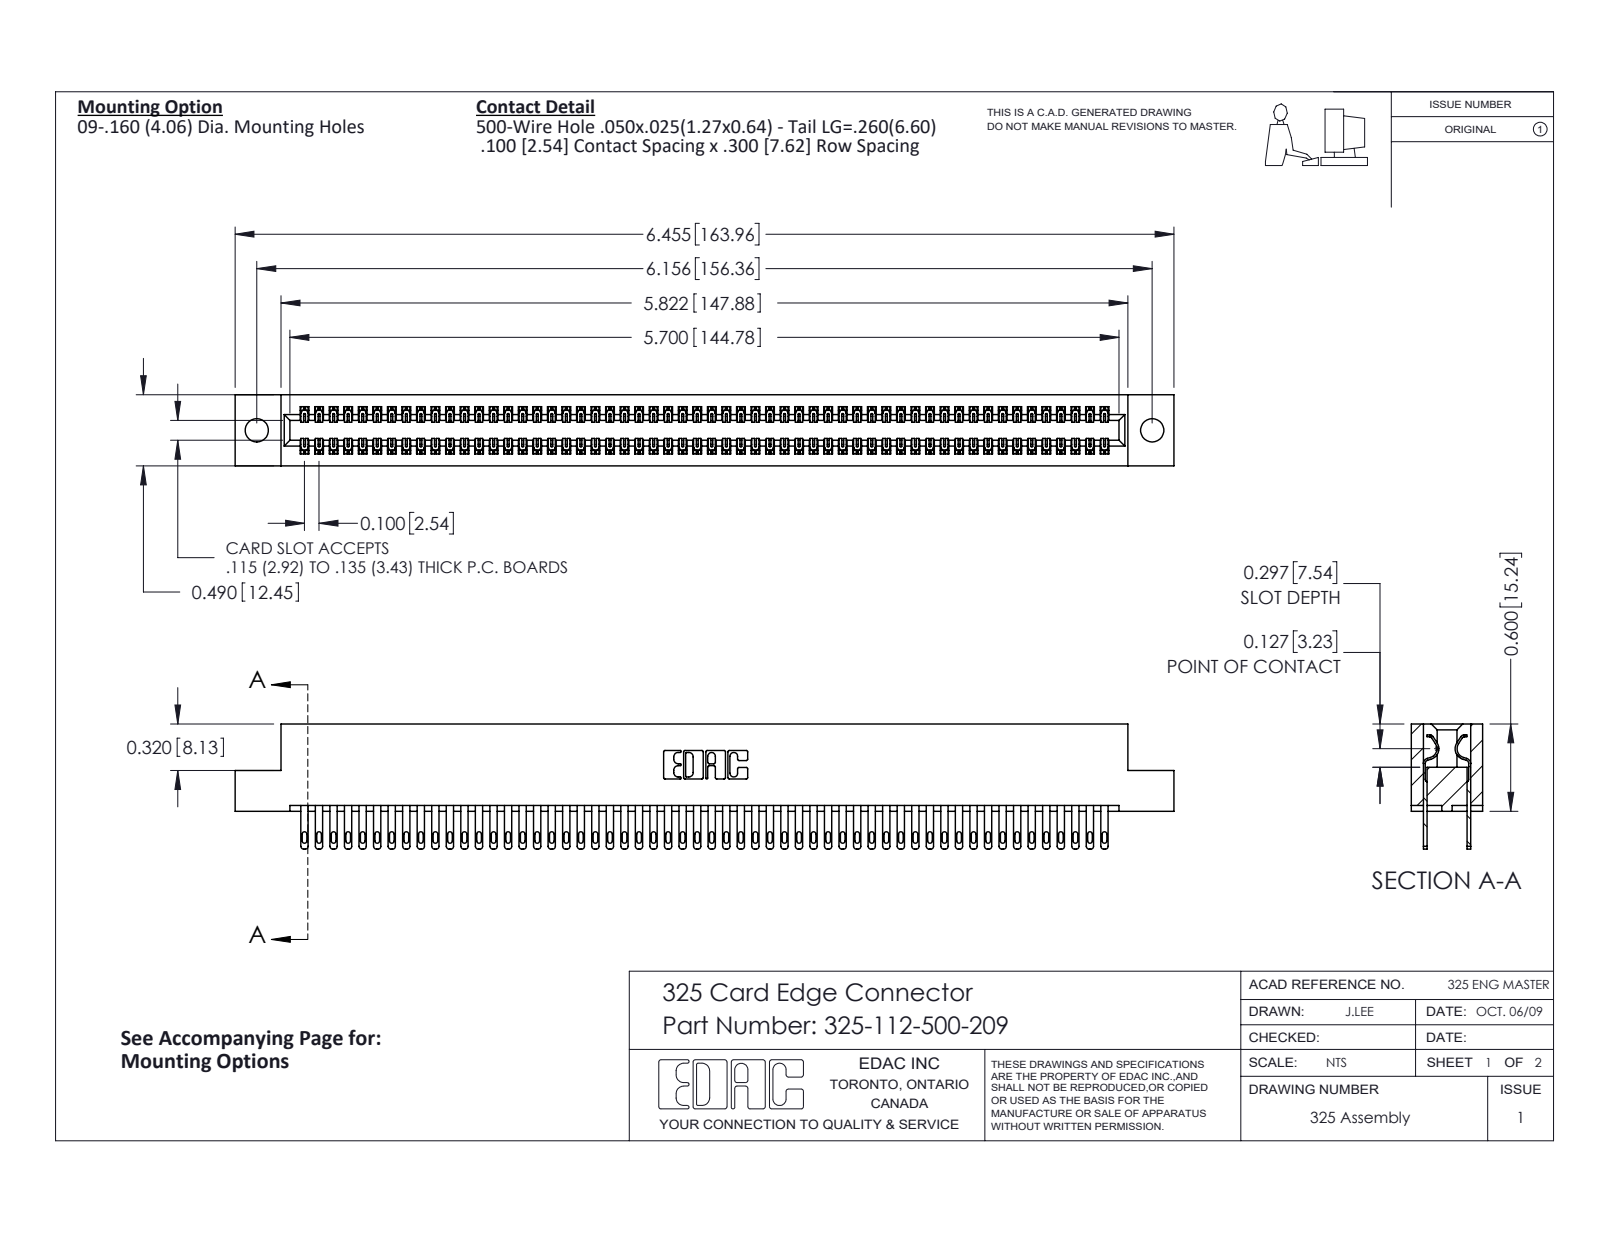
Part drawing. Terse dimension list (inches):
name: 325 Part_.160 TH; 325-112-500-209; 325-292-001_325-293-100
written by: SolidWorks 2016 (CONFIG_CONTROL_DESIGN)
unit: in
bodies: 113 solids, 5490 faces (3430 planar, 2060 cylindrical, 0 other)
size: 6.455 × 0.86 × 0.49
volume: 1.306 in³; area: 42.36 in²
holes: 2× ⌀0.16
rounds: 168× R0.006, 112× R0.016, 112× R0.02, 22× R0.01, 6× R0.007, 6× R0.031, 3× R0.026, 2× R0.014
face distances: 0.083, 0.407, 0.3, 0.107, 0.383, 0.025, 0.49, 0.325, 0.275, 0.263
hole spacings: 6.156
